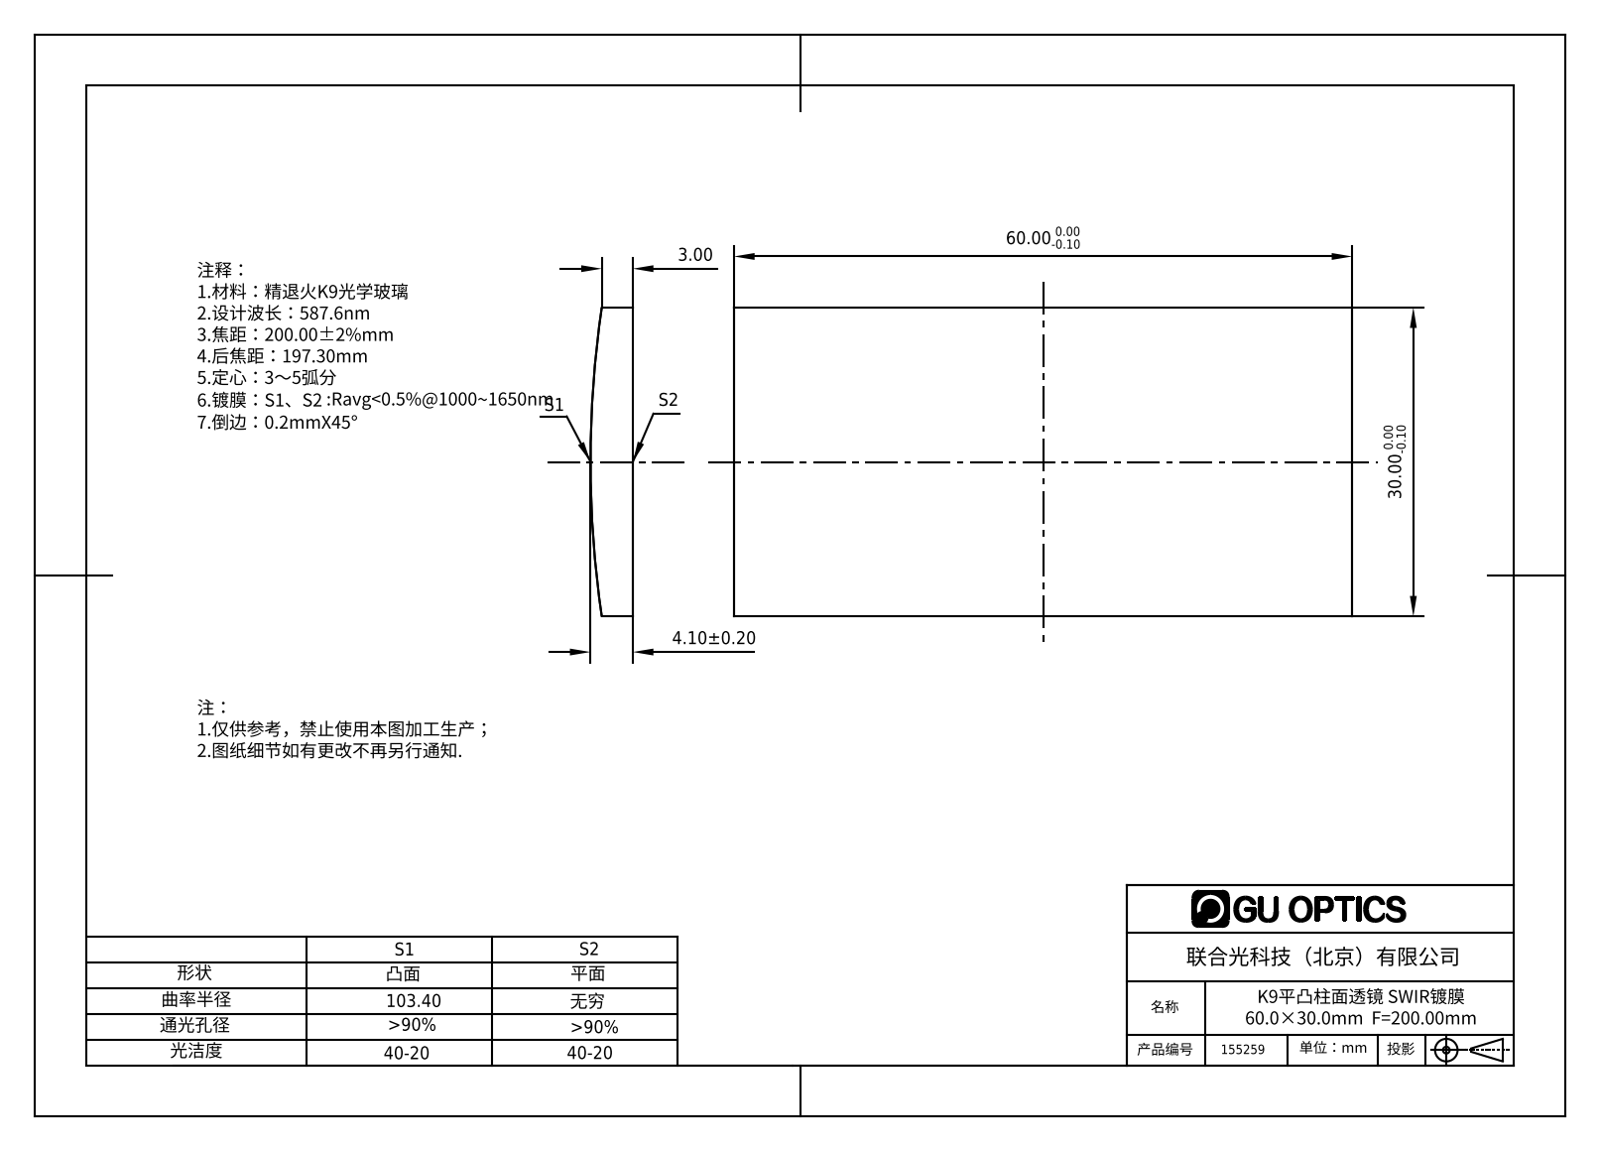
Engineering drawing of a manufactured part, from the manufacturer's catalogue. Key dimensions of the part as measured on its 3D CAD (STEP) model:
Part name (STEP PRODUCT): 155061
STEP written by: SolidWorks 2016 (AUTOMOTIVE_DESIGN)
Units: millimetres
Bodies: 1 solid, 6 faces (5 planar, 1 cylindrical, 0 other)
Overall size (bounding box): 60 × 30 × 4.1
Volume: 6 725 mm³ · Surface area: 4 191 mm²
Partial cylindrical surfaces — rounded edges, fillets, slot ends (radius × count): R103.4 ×1
Main face-to-face distances: 30, 60
